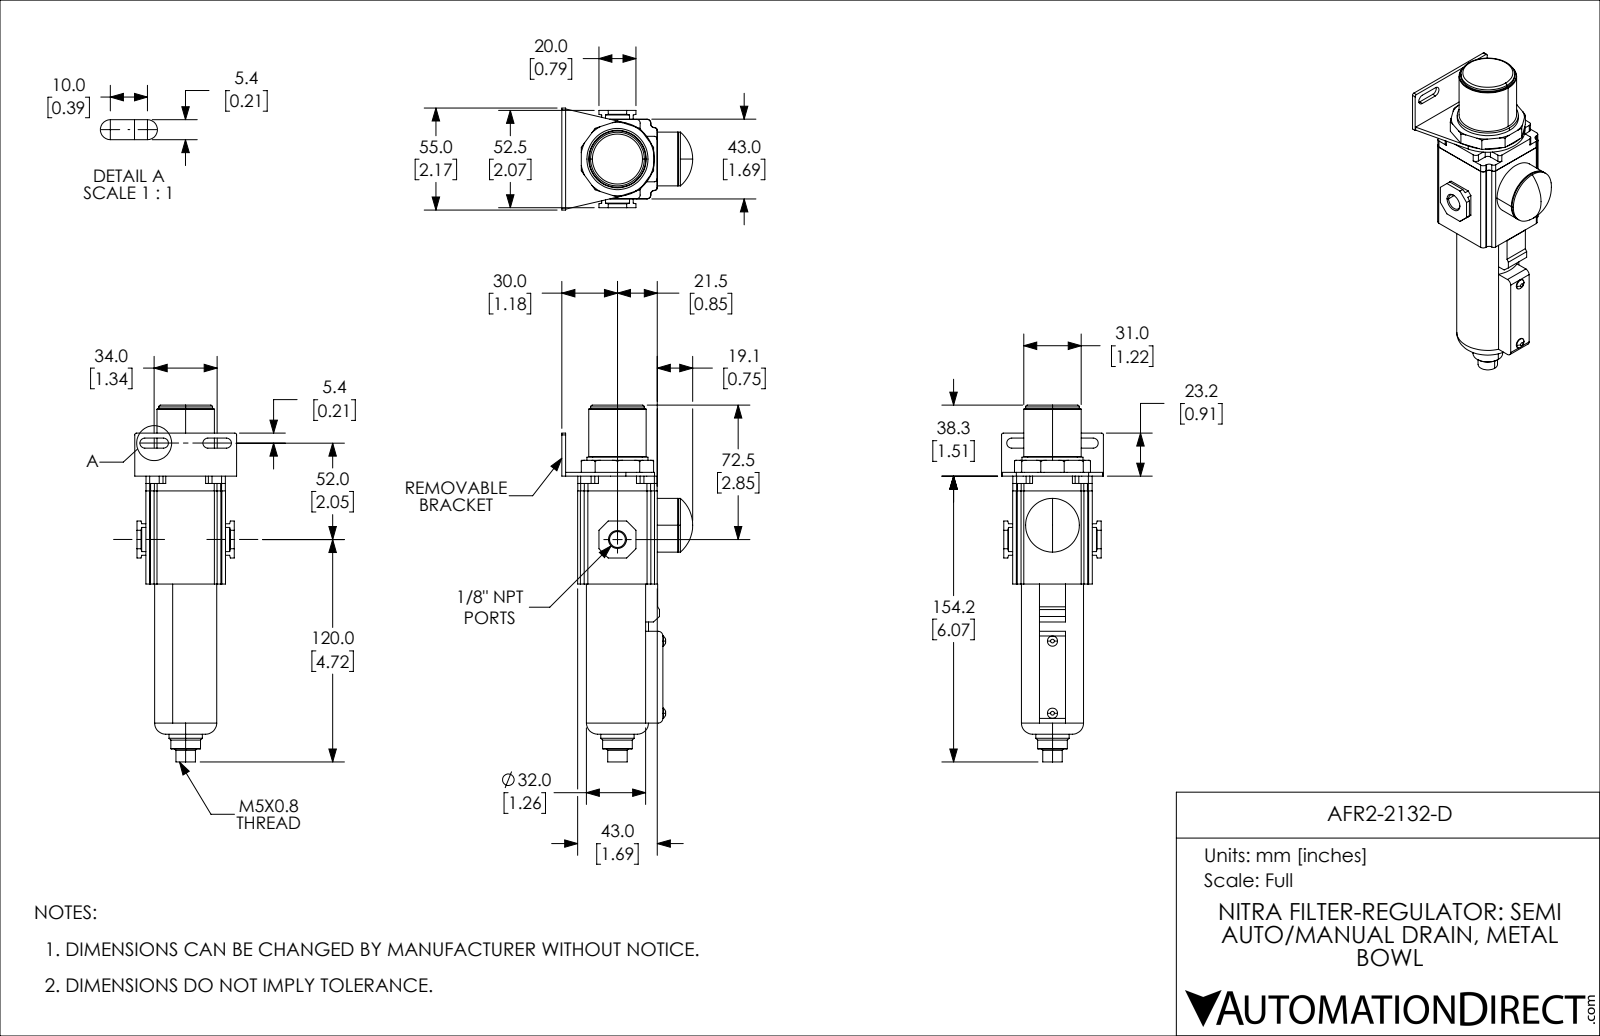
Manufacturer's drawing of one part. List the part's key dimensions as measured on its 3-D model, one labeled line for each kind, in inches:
Part name (STEP PRODUCT): AFR2-2132-D
STEP written by: SolidWorks 2019 (CONFIG_CONTROL_DESIGN)
Units: inches
Bodies: 1 solid, 237 faces (126 planar, 75 cylindrical, 36 other)
Overall size (bounding box): 7.579 × 2.78 × 2.165
Volume: 14.15 in³ · Surface area: 52.85 in²
Round holes (diameter × count): ⌀0.163 ×1, ⌀0.337 ×1
Round bosses / shafts (diameter × count): ⌀1.142 ×2, ⌀0.217 ×2, ⌀1.319 ×1, ⌀1.299 ×1, ⌀1.22 ×1, ⌀1.054 ×1, ⌀0.709 ×1, ⌀0.63 ×1
Partial cylindrical surfaces — rounded edges, fillets, slot ends (radius × count): R0.079 ×24, R0.059 ×12, R0.106 ×4, R0.039 ×2, R0.098 ×2, R0.787 ×1
Main face-to-face distances: 1.693, 0.079, 0.335, 0.256, 0.571, 1.122, 1.949, 2.067, 2.028, 1.689
